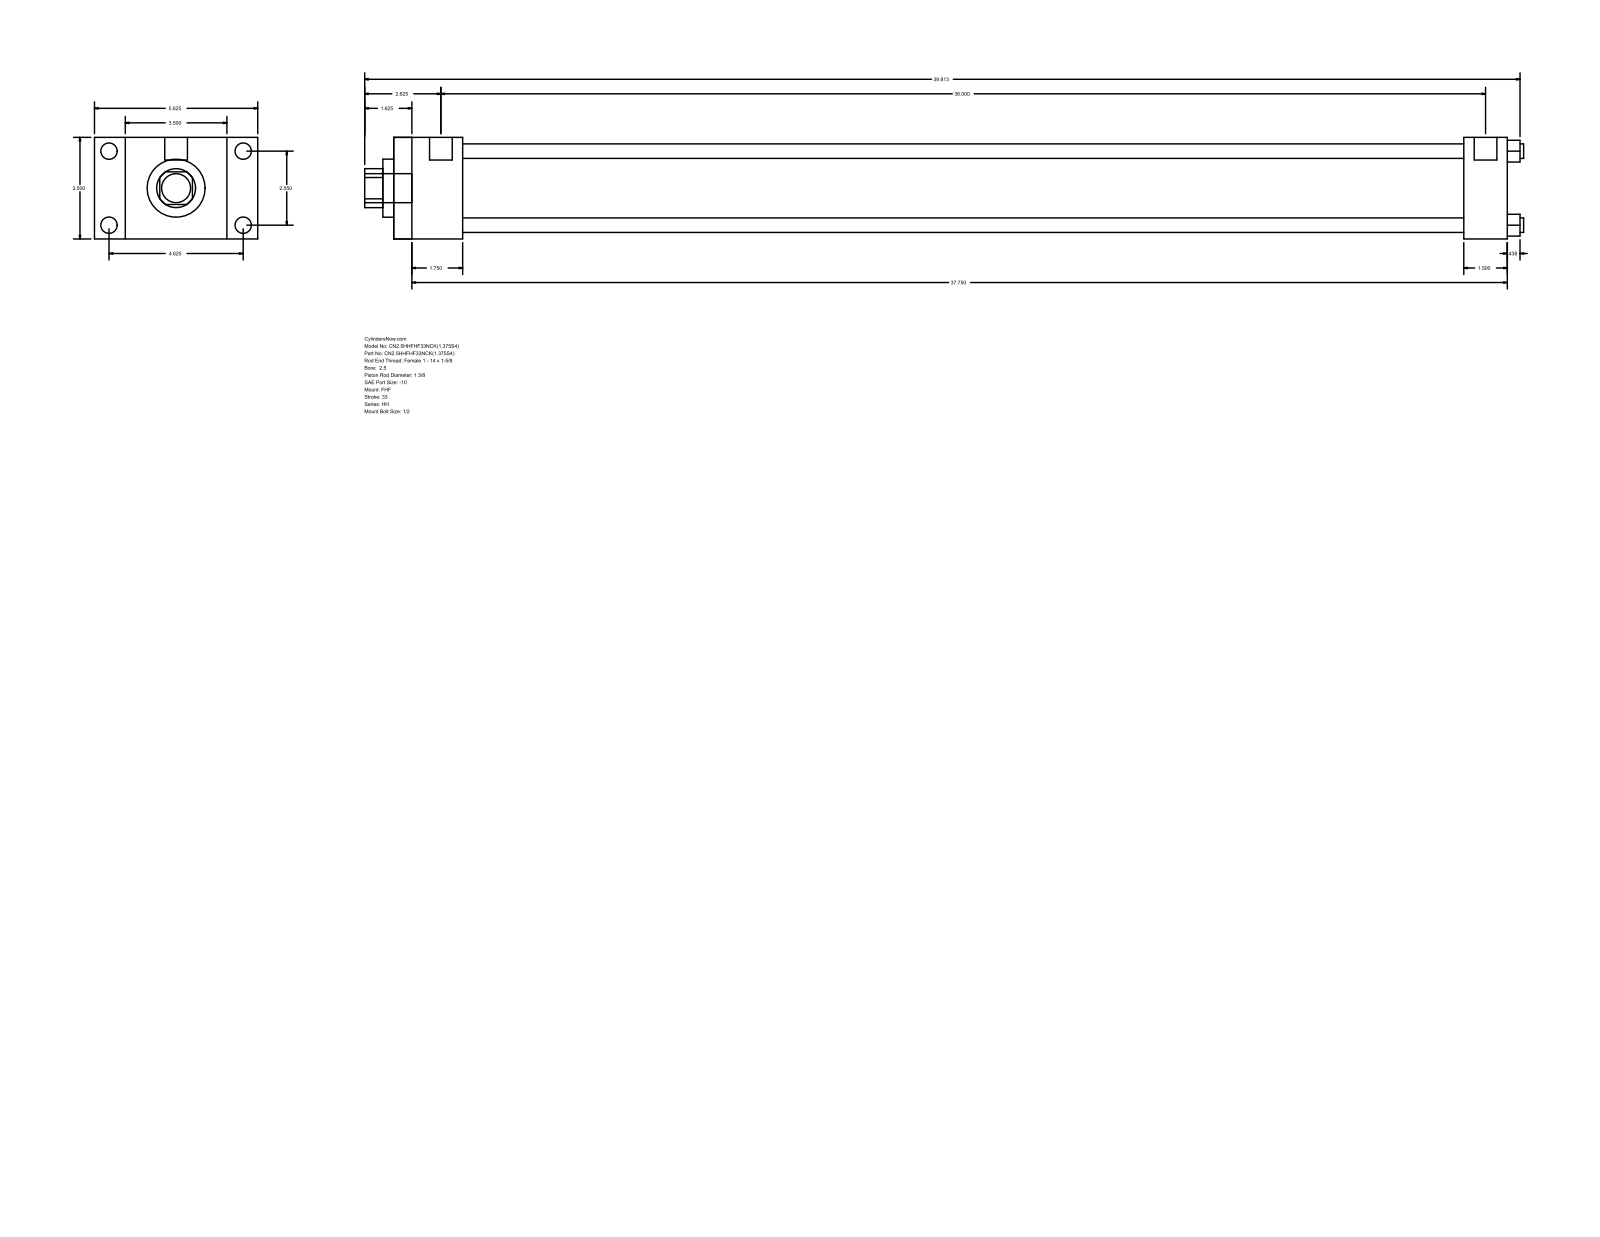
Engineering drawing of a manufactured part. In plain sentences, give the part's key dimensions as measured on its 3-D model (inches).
The part is named "HH_FHF__0250_1.375". Its 3-D file was written by "GSSL Pune (CONFIG_CONTROL_DESIGN)". It is 0 solids with 88 faces: 60 planar, 28 cylindrical and 0 other. Overall it measures 39.937 by 5.625 by 3.5 inches. Round holes: 4 of diameter 0.5, 1 of diameter 1.375, 1 of diameter 2, 1 of diameter 2.875. Round bosses or shafts: 4 of diameter 0.563, 4 of diameter 0.219, 2 of diameter 0.781, 1 of diameter 1. Partial cylindrical surfaces (rounded edges, fillets, slot ends): 1 of radius 0.672. The main face-to-face distances are 3.5, 2.375, 1.063, 4.563, 38.375, 36, 5.625, 36.875, 34.5, 1.5. The hole center spacings are 1.803, 2.55, 3.606.
